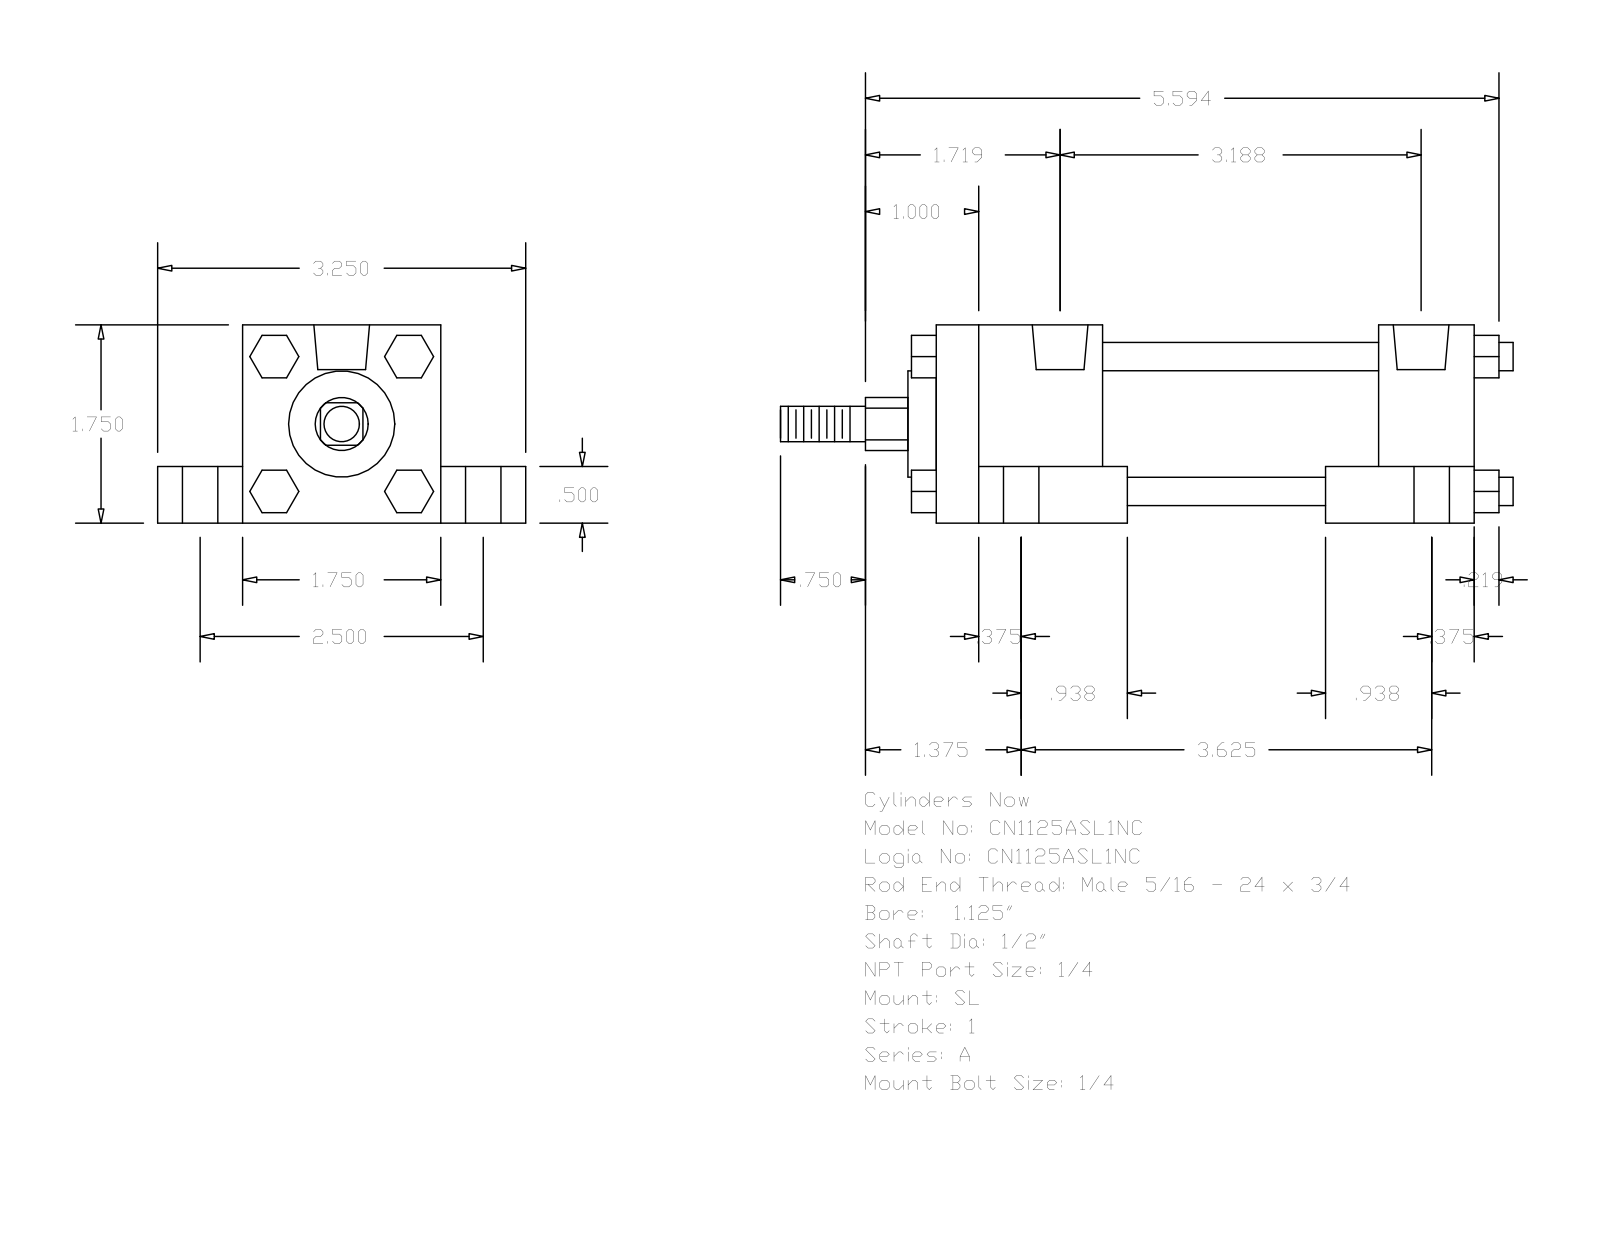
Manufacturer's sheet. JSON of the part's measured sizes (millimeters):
{"part_name": "A_SL__0112_0.5", "step_written_by": "GSSL Pune (CONFIG_CONTROL_DESIGN)", "units": "millimeters", "bodies": {"solids": 0, "faces": 150, "planar": 114, "cylindrical": 36, "other": 0}, "overall_size": [164.31, 82.55, 44.45], "round_holes": [[5.56, 4], [7.94, 4], [14.29, 4], [12.49, 2]], "round_bosses_or_shafts": [[6.35, 4], [31.88, 1], [23.81, 1], [12.7, 1], [7.94, 1]], "partial_cylinders_radius": [[5.94, 1]], "face_to_face_distances": [44.46, 31.76, 12.7, 19.04, 63.5, 120.65, 99.21, 21.44, 37.3, 61.91], "hole_center_spacings": [31.84, 32, 32.93, 33.39, 63.5, 77.79, 87.71, 89.18]}
